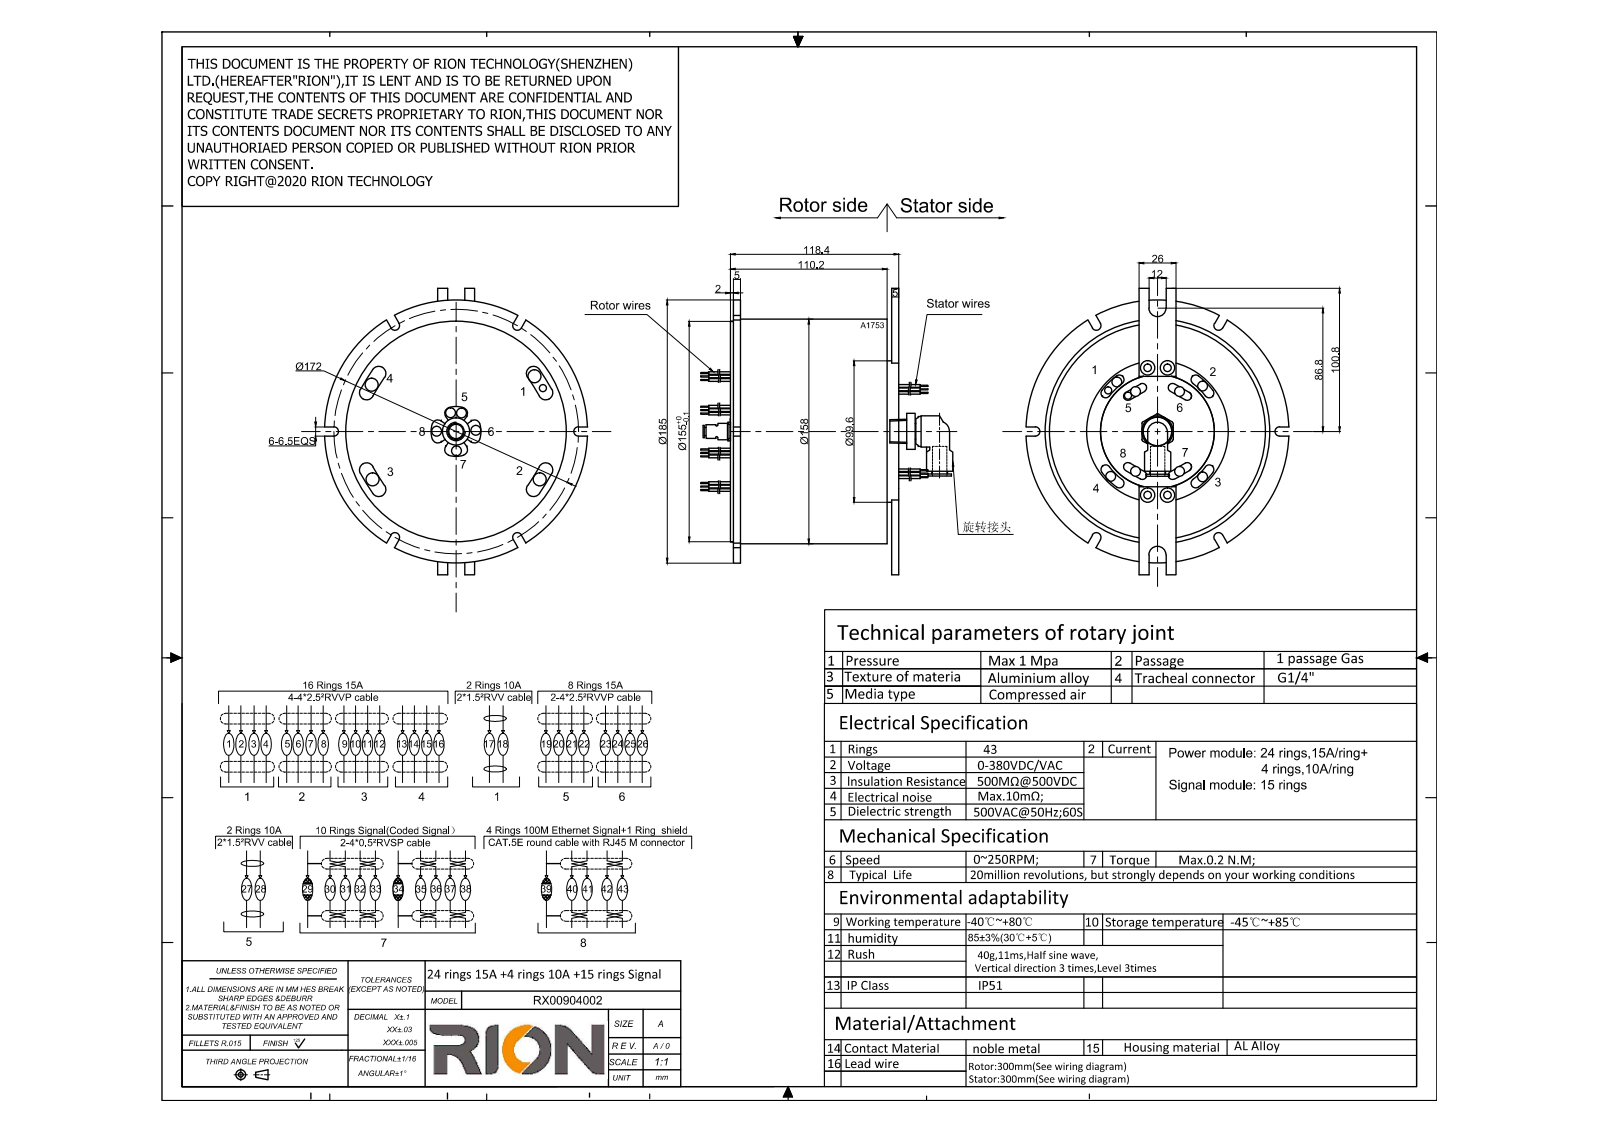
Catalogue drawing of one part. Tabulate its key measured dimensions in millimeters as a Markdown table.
| quantity | value |
| --- | --- |
| part name | KSL10-02S; RX00904002; MAPH100-03-G1001-P2415-P0410-S10-1E(A1753)-1_1; KQ2S10-02S |
| STEP written by | SolidWorks 2014 (AUTOMOTIVE_DESIGN) |
| units | millimeters |
| bodies | 5 solids, 378 faces (146 planar, 200 cylindrical, 32 other) |
| overall size | 201.6 × 189.65 × 184.89 |
| volume | 2 292 000 mm³ |
| surface area | 150 325 mm² |
| round holes (diameter × count) | 5.2 × 4, 8 × 3, 10 × 2, 11.8 × 2, 11 × 1, 152 × 1 |
| round bosses / shafts (diameter × count) | 7 × 13, 9 × 4, 5 × 3, 185 × 1, 158 × 1, 155 × 1, 151.6 × 1, 99.6 × 1 |
| partial cylindrical surfaces (radius × count) | 3.25 × 14, 3 × 8, 4 × 8, 5 × 8, 271.71 × 4, 271.76 × 4, 6 × 2, 9.5 × 1 |
| main face-to-face distances | 110.2, 5, 111.4, 8.2, 118.4, 7, 116.4, 103.2, 2, 108.2 |
| hole center spacings | 45.34, 14, 45.38, 89.6, 90.69, 0.33, 45.13, 45.2 |
